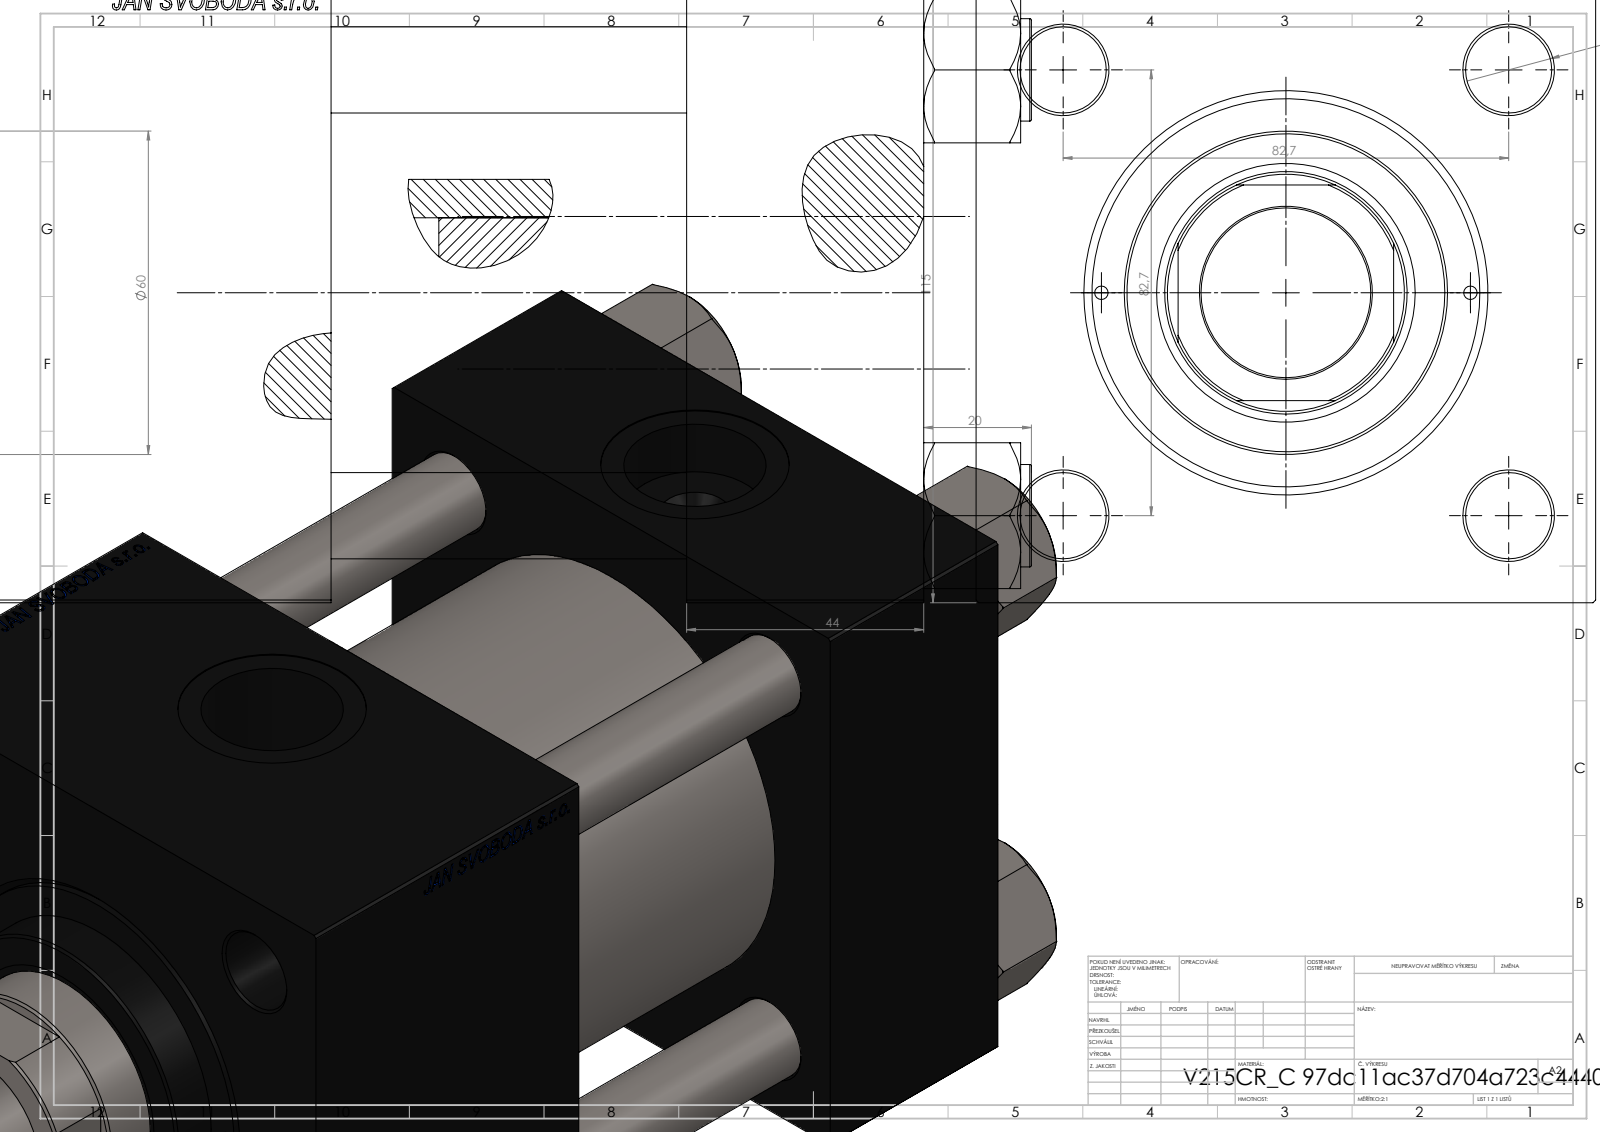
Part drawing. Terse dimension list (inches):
name: V215CR_C_Body; V215CR_VCP_C; V215_VC_A; V215CR_C_TYCINKA (+1 more)
written by: SolidWorks 2019 (CONFIG_CONTROL_DESIGN)
unit: in
bodies: 11 solids, 1203 faces (576 planar, 91 cylindrical, 536 other)
size: 9.055 × 4.528 × 4.528
volume: 111 in³; area: 424.6 in²
holes: 4× ⌀0.63, 2× ⌀0.098, 2× ⌀0.276, 2× ⌀1.041, 2× ⌀1.378, 1× ⌀1.24, 1× ⌀1.772, 1× ⌀1.89, 1× ⌀2.402, 1× ⌀2.835, 1× ⌀3.15
bosses: 4× ⌀0.748, 1× ⌀3.386, 1× ⌀2.362
rounds: 1× R0.866
face distances: 4.528, 1.732, 4.331, 7.047, 5.315, 2.598, 2.717, 0.787, 5.917, 4.185
hole spacings: 1.652, 2.302, 3.256, 3.393, 1.348, 4.605, 2.697, 4.37
